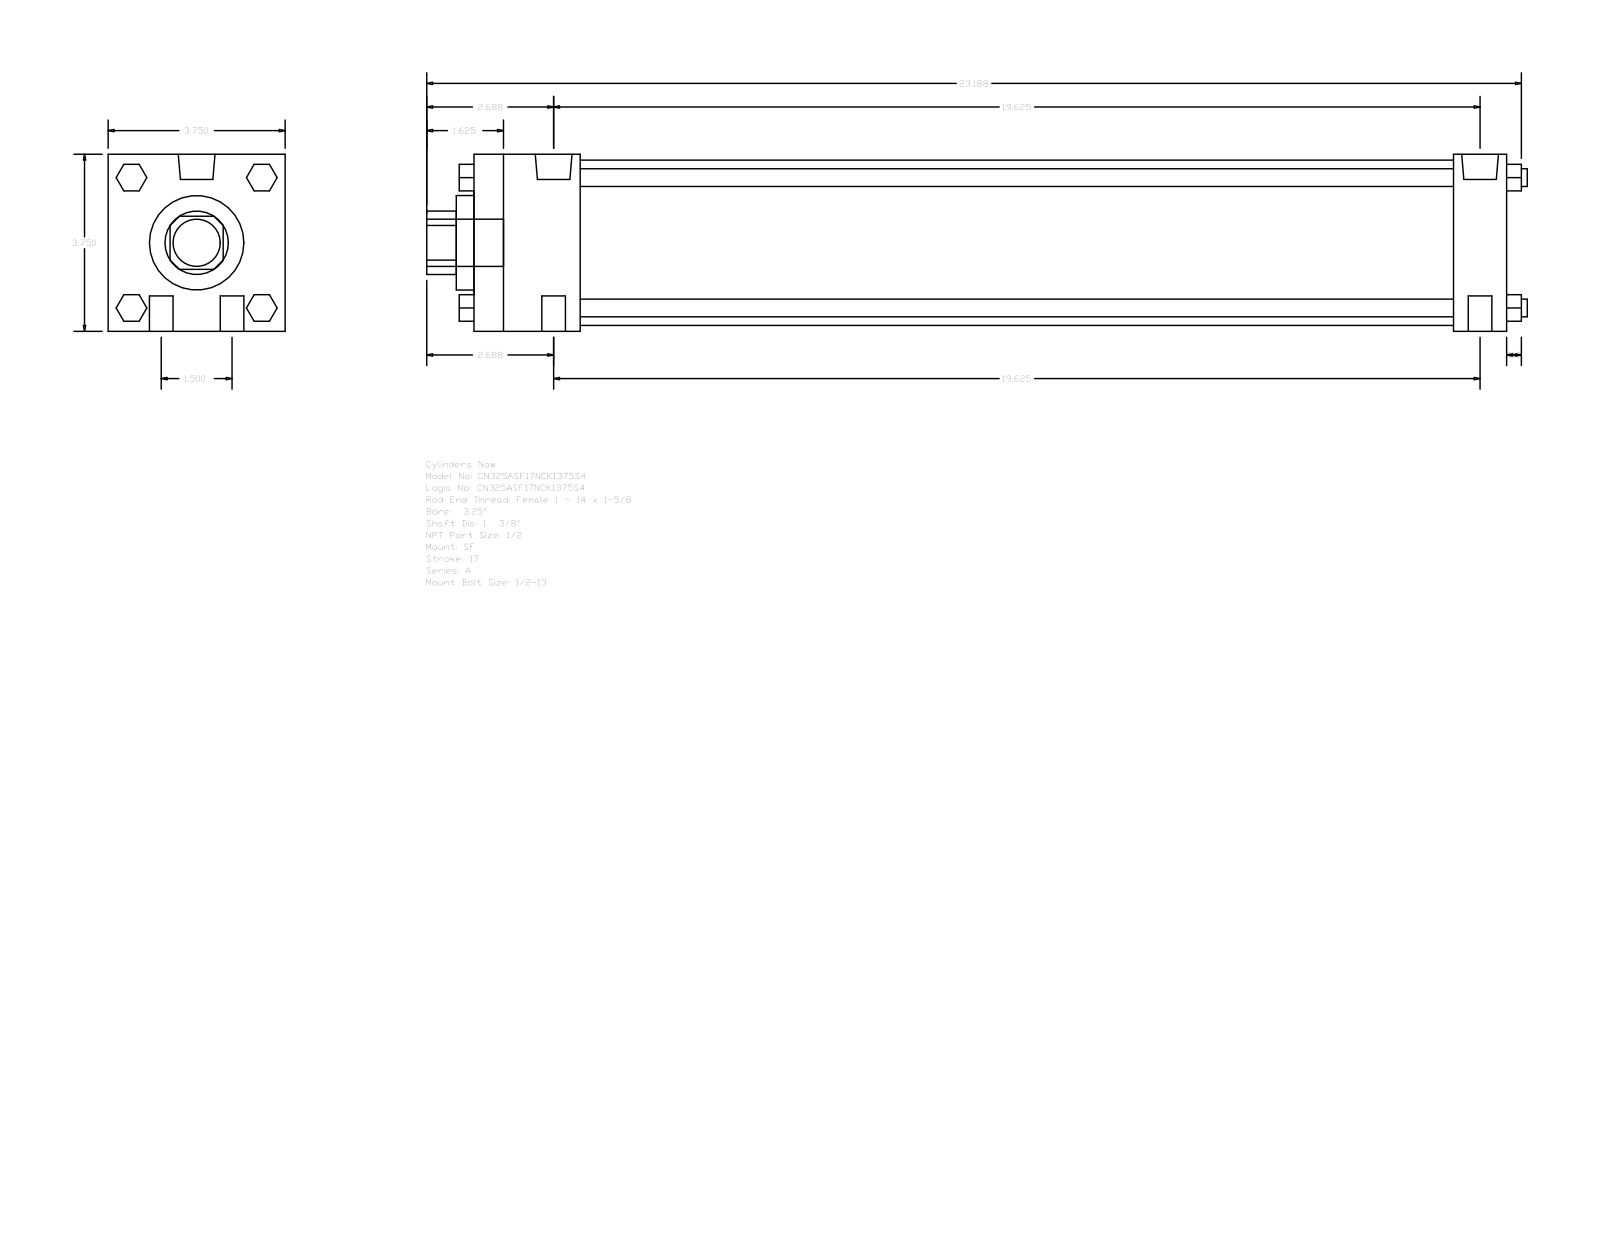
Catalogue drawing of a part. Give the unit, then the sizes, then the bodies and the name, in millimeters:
Units: millimetres
Overall size (bounding box): 592.14 × 95.25 × 95.25
Round holes (diameter × count): ⌀34.92 ×1, ⌀50.8 ×1, ⌀88.9 ×1
Round bosses / shafts (diameter × count): ⌀12.7 ×4, ⌀9.53 ×4, ⌀19.77 ×2, ⌀8.73 ×2, ⌀25.4 ×1
Partial cylindrical surfaces — rounded edges, fillets, slot ends (radius × count): R17.06 ×1
Main face-to-face distances: 95.24, 555.62, 28.57, 527.05, 57.15, 469.9, 498.47, 9.52, 66.67, 536.57
Bodies: 0 solids, 124 faces (94 planar, 30 cylindrical, 0 other)
Part name (STEP PRODUCT): A_SF__0325_1.375
STEP written by: GSSL Pune (CONFIG_CONTROL_DESIGN)
